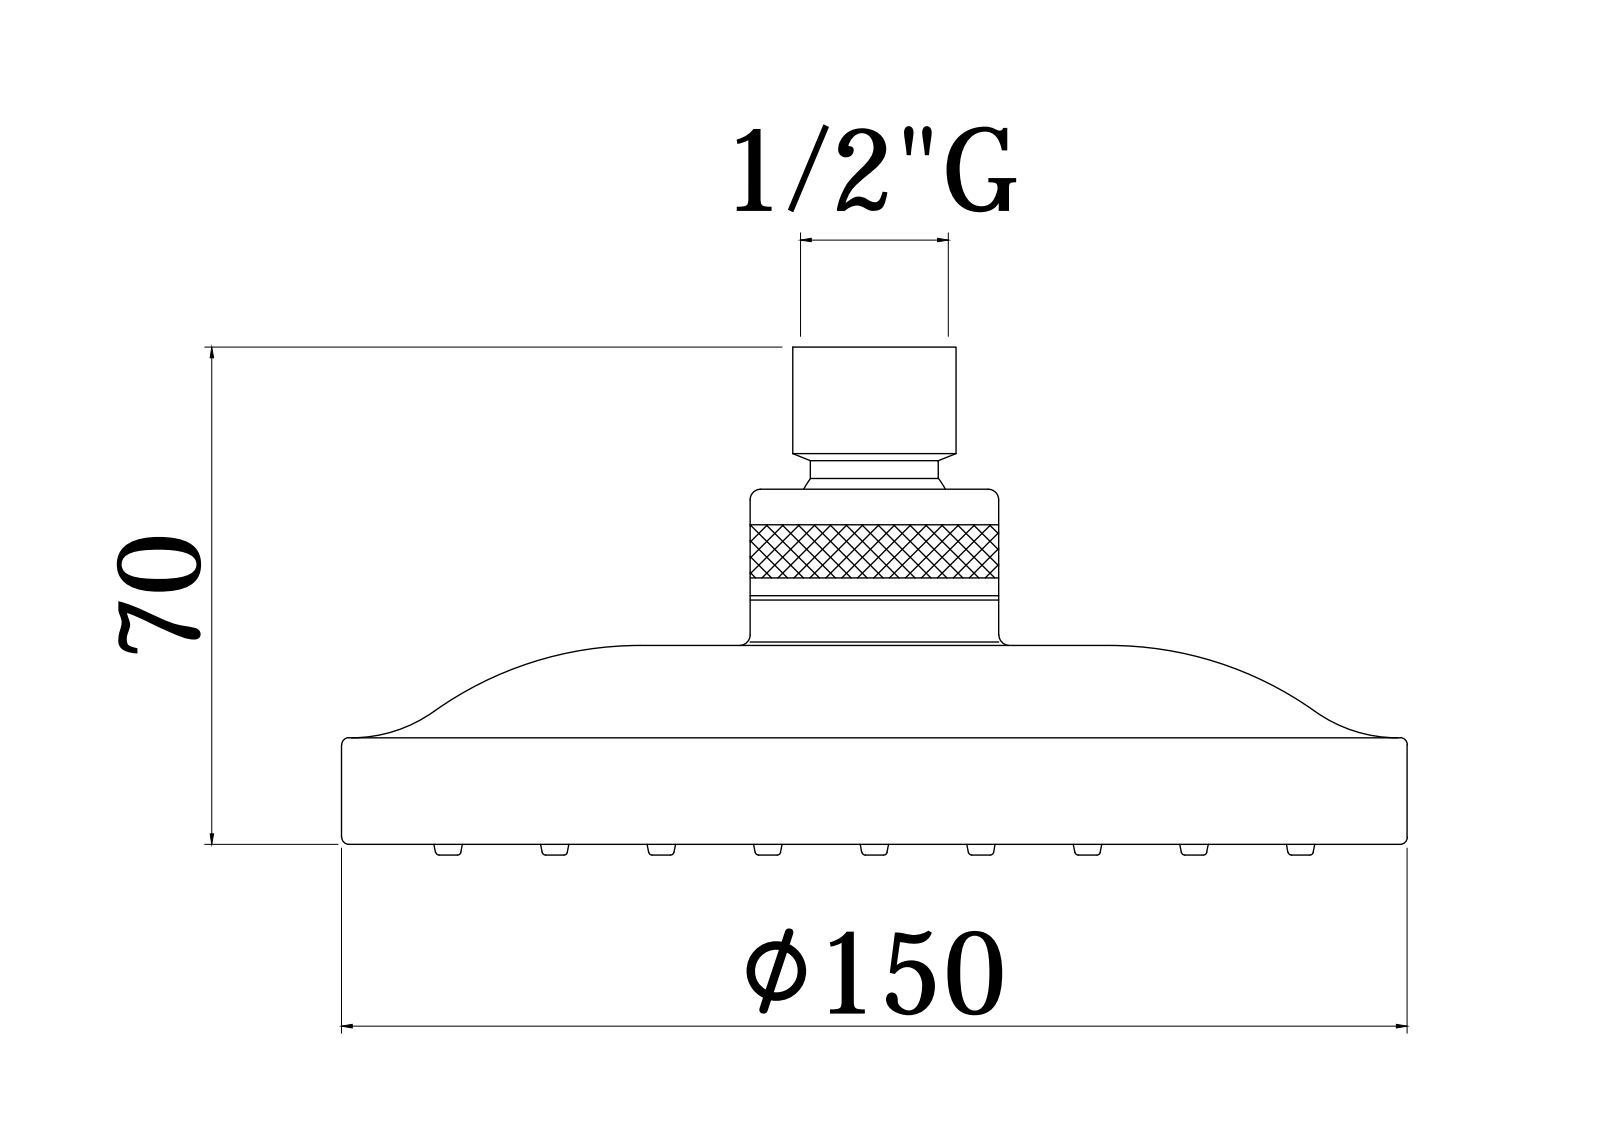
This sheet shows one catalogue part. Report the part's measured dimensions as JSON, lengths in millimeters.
{"part_name": "ZSOF029CR", "step_written_by": "CREO PARAMETRIC BY PTC INC, 2020044 (CONFIG_CONTROL_DESIGN)", "units": "millimeters", "bodies": {"solids": 2, "faces": 5873, "planar": 3818, "cylindrical": 1043, "other": 1012}, "overall_size": [149.99, 149.99, 75.95], "volume_mm3": 191182, "surface_area_mm2": 121448, "round_holes": [[4.5, 6], [3.5, 1], [4, 1], [5, 1], [6.8, 1], [11.4, 1], [12.2, 1], [12.8, 1], [13.95, 1], [14.67, 1], [16.1, 1], [16.15, 1]], "round_bosses_or_shafts": [[145, 1], [144.6, 1], [137.46, 1], [35.5, 1], [28.4, 1], [28.1, 1], [25.2, 1], [23, 1]], "partial_cylinders_radius": [[1, 1], [11, 1], [14.08, 1], [14.97, 1]], "face_to_face_distances": [13.6, 2.6, 3, 11, 18.2, 15, 21.2, 3.5, 30, 27], "hole_center_spacings": [56.18, 97.3, 56.17, 112.35]}
